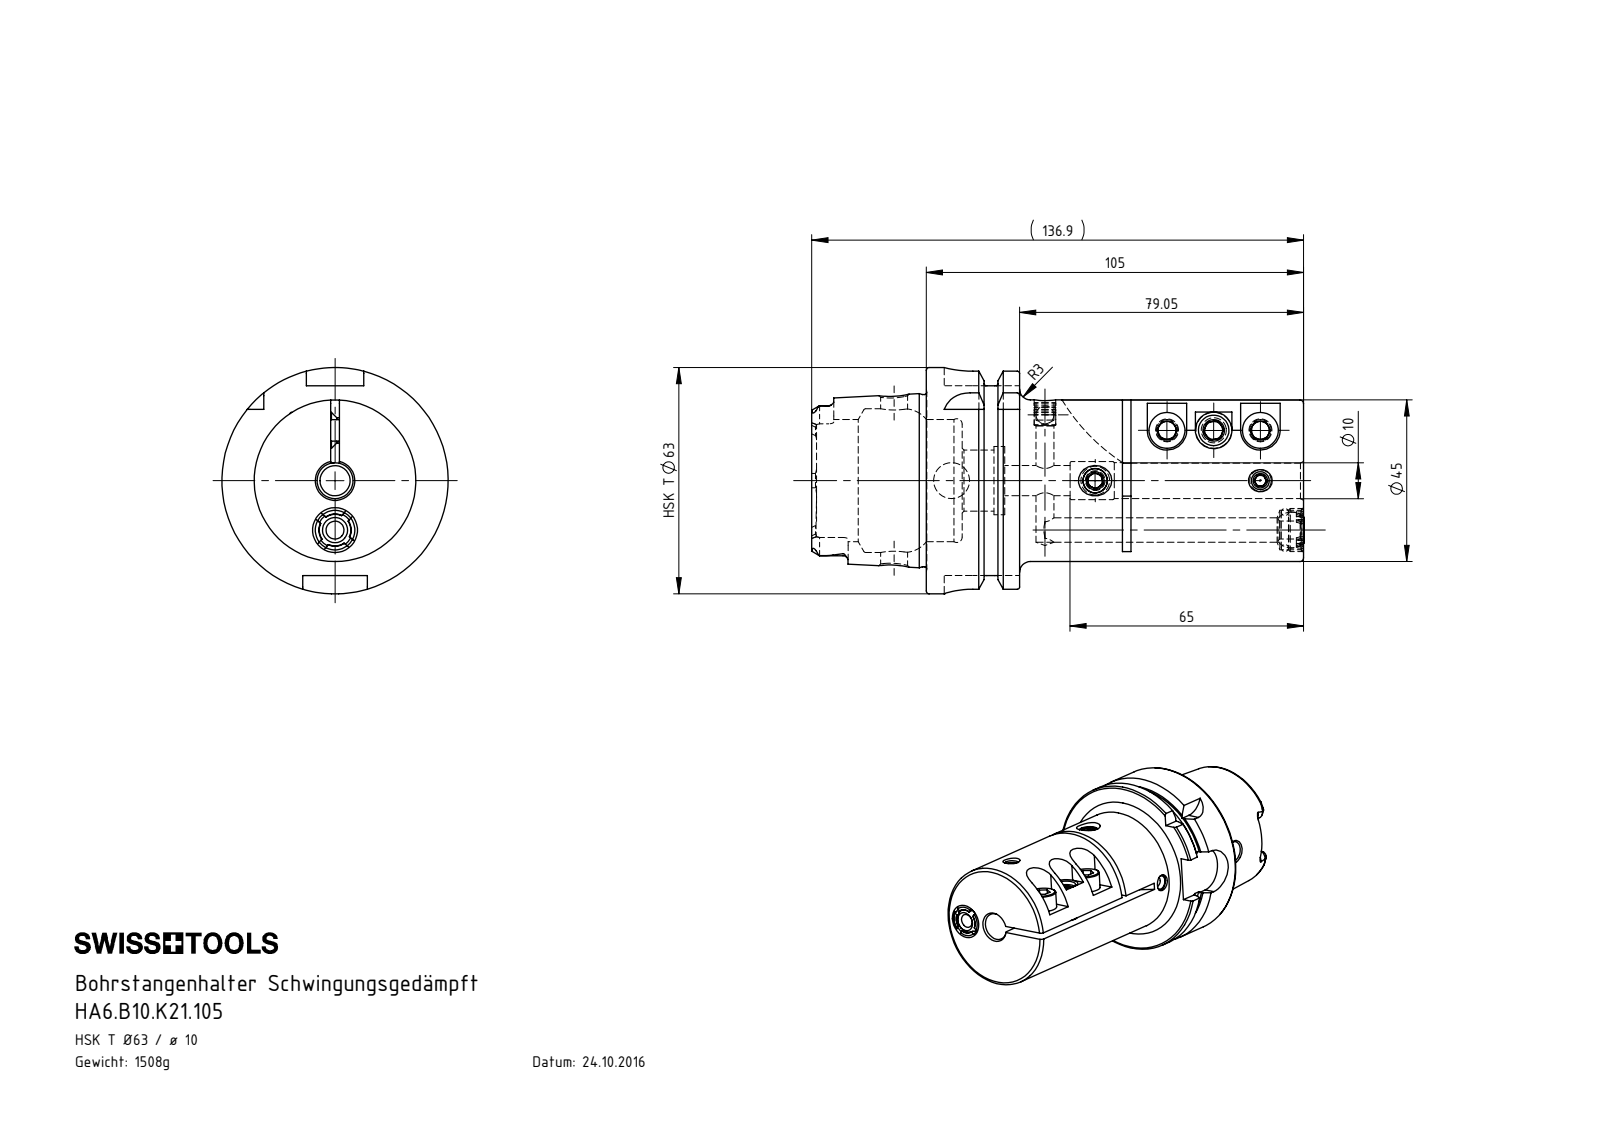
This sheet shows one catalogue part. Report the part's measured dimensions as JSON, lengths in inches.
{"part_name": "DIN 3771 - 8x2; KU1-U12.002.010; ISO 4028 - M8 x 16; ISO 4027 - M6 x 16_PreviewCfg (+7 more)", "step_written_by": "SolidWorks 2015 (CONFIG_CONTROL_DESIGN)", "units": "inches", "bodies": {"solids": 11, "faces": 469, "planar": 154, "cylindrical": 122, "other": 193}, "overall_size": [5.409, 2.48, 2.48], "volume_in3": 11.73, "surface_area_in2": 72.1, "round_holes": [[0.197, 5], [0.394, 3], [0.252, 2], [0.268, 2], [0.157, 1], [0.295, 1], [0.331, 1], [0.335, 1], [0.417, 1], [0.433, 1], [0.669, 1], [0.748, 1]], "round_bosses_or_shafts": [[0.236, 4], [0.394, 3], [2.48, 1], [2.163, 1], [1.887, 1], [1.772, 1], [0.472, 1], [0.315, 1]], "partial_cylinders_radius": [[0.055, 6], [0.113, 4], [0.315, 4], [0.217, 2], [0.173, 1], [0.201, 1], [2.047, 1], [2.165, 1]], "face_to_face_distances": [0.094, 4.134, 1.022, 3.112, 0.63, 2.15, 1.128, 1.984, 2.244, 1.222], "hole_center_spacings": [0.512, 0.541, 0.551, 0.752, 0.961, 1.024, 1.163, 1.411]}
